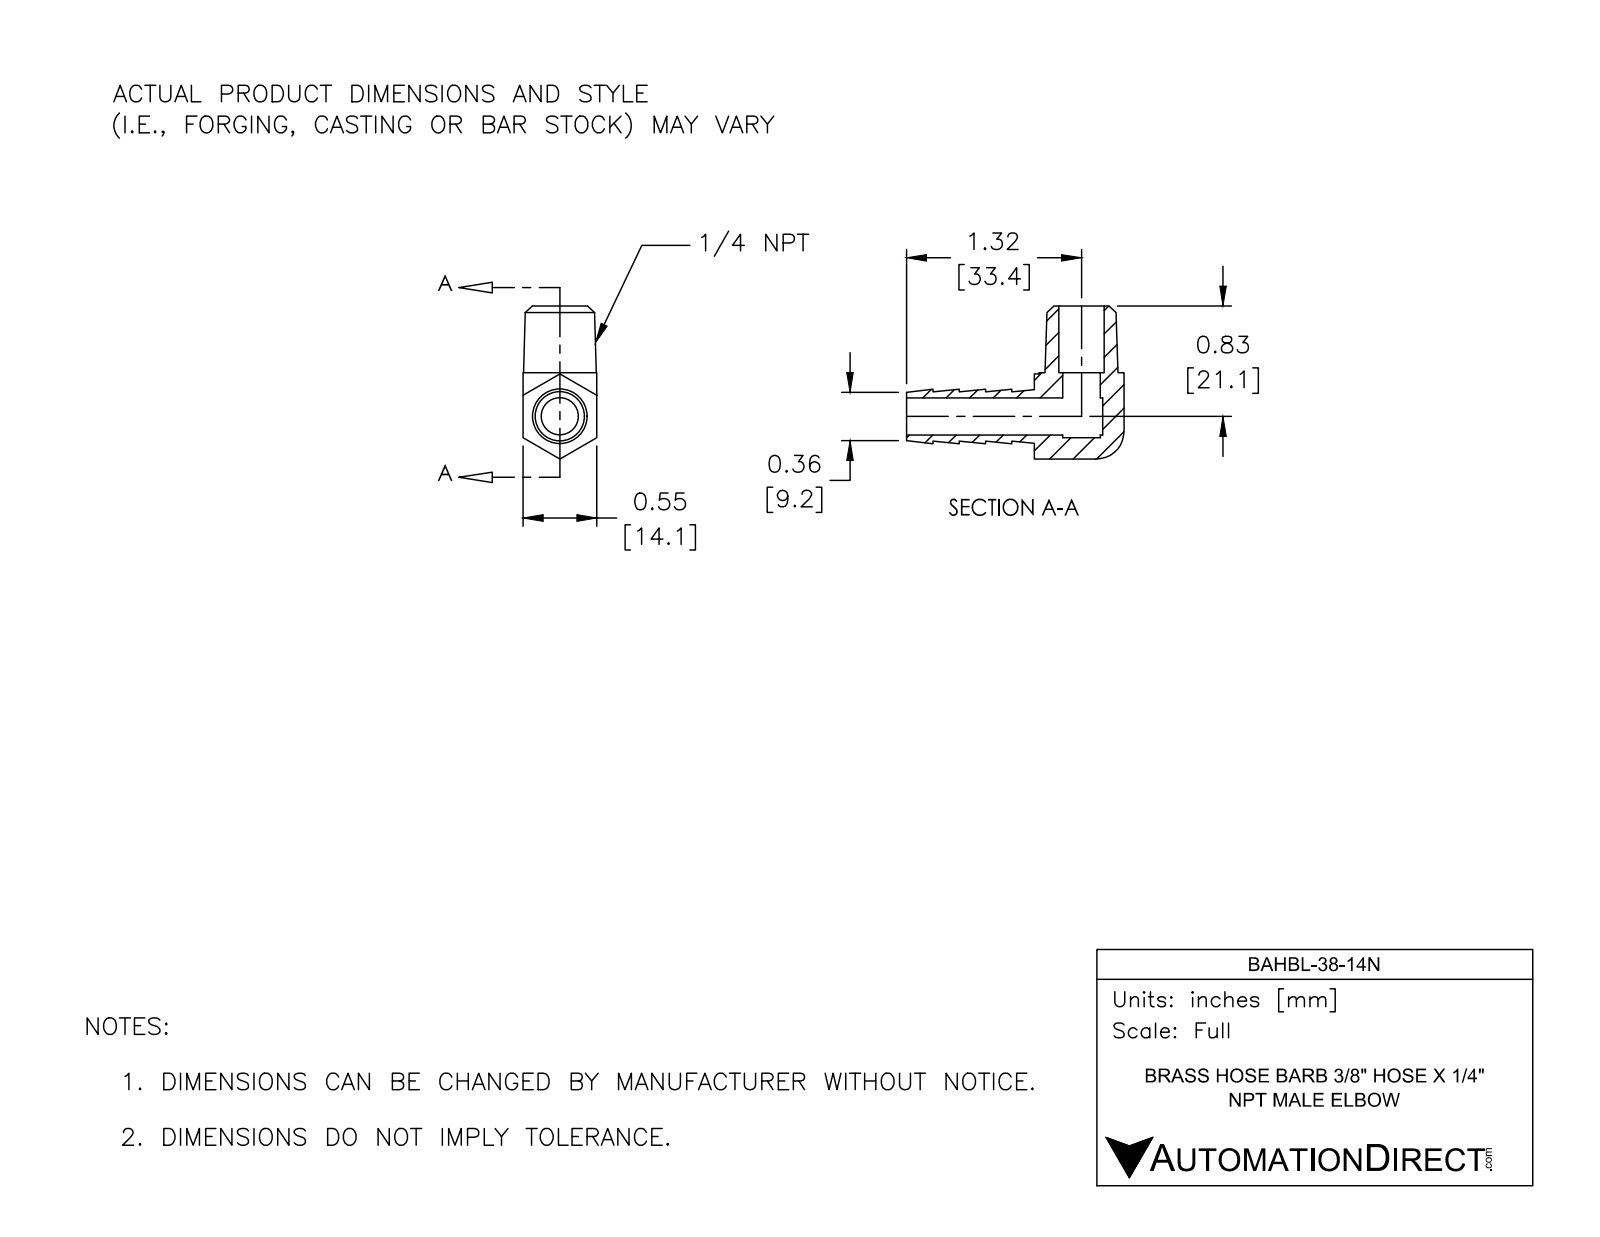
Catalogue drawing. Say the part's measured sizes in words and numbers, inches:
The part is named "BAHBL-38-14N". Its 3-D file was written by "SolidWorks 2017 (AUTOMOTIVE_DESIGN)". It is 1 solid with 45 faces: 21 planar, 10 cylindrical and 14 other. Overall it measures 1.636 by 1.151 by 0.554 inches. Its volume is 0.25 cubic inches and its surface area 5.753 square inches. Round holes: 1 of diameter 0.278, 1 of diameter 0.283, 1 of diameter 0.341. Partial cylindrical surfaces (rounded edges, fillets, slot ends): 2 of radius 0.25. The main face-to-face distances are 0.554, 0.198, 0.554, 0.396, 0.515, 0.489, 0.594, 1.476, 0.961, 0.991.
